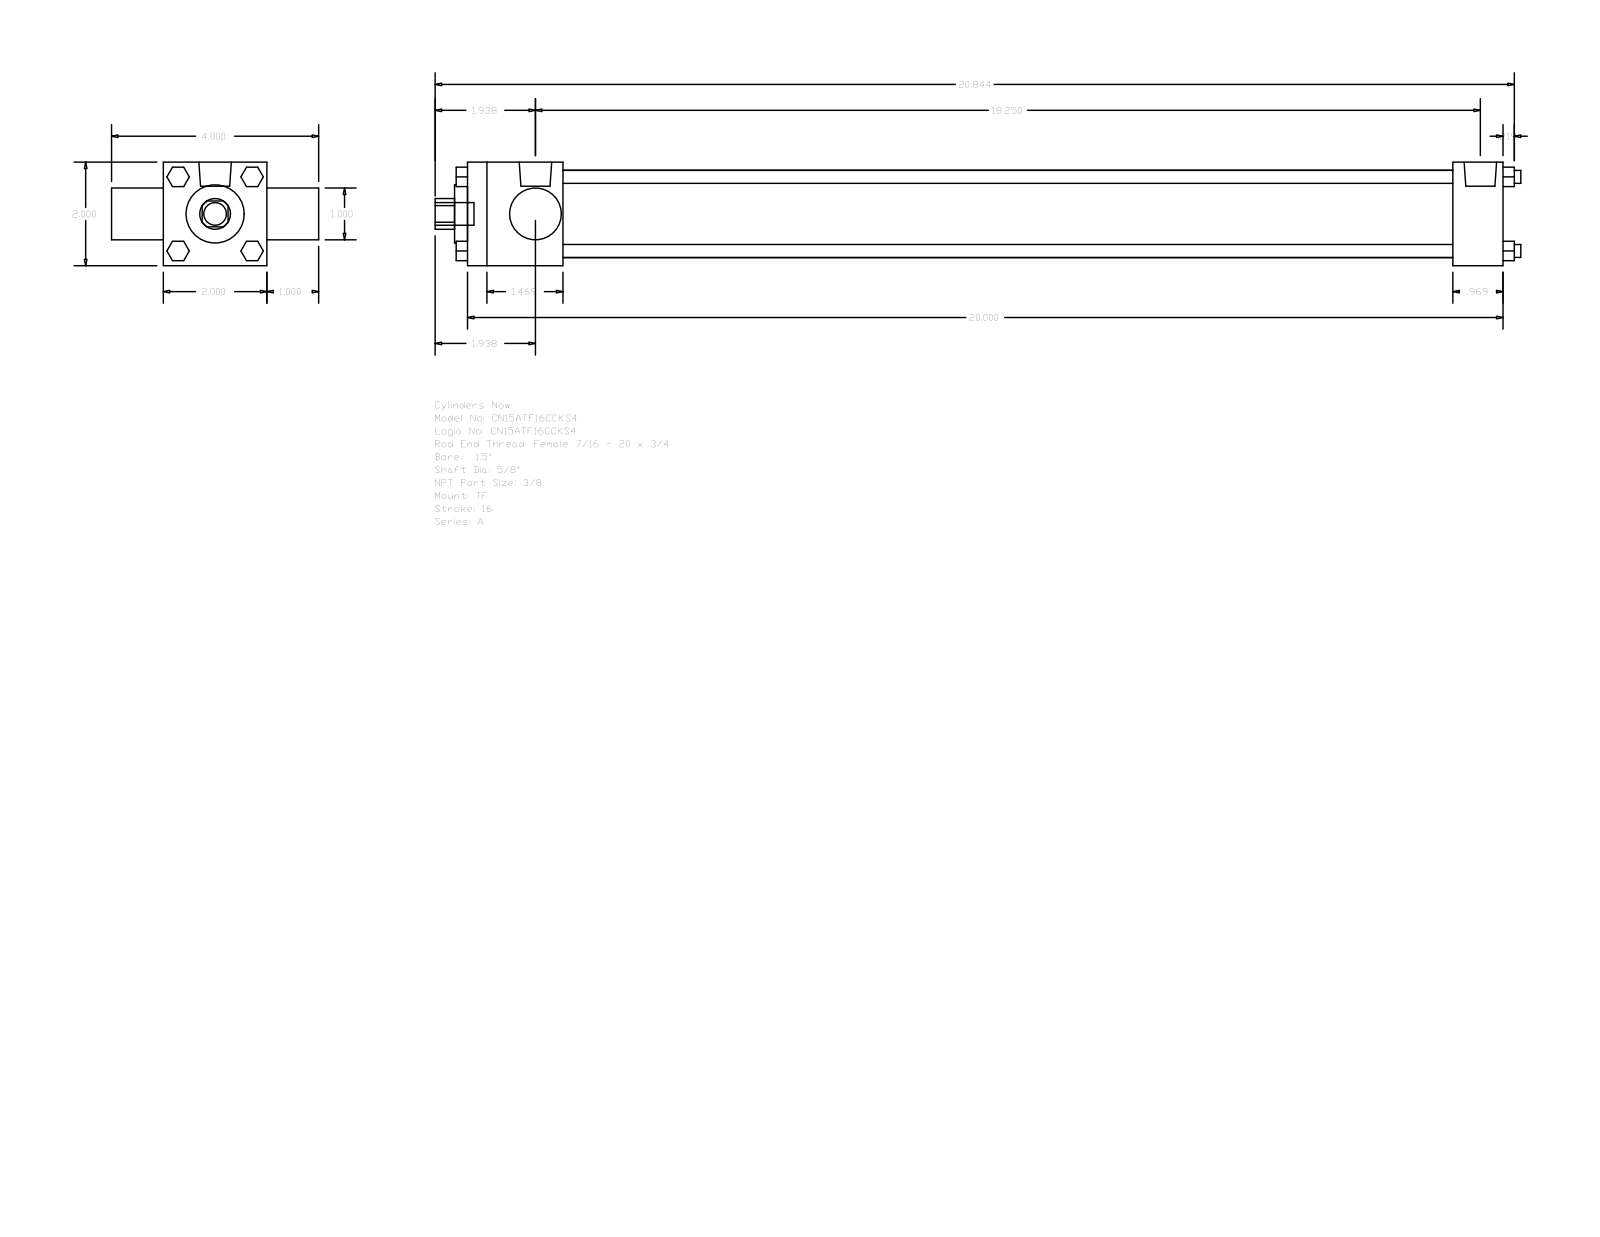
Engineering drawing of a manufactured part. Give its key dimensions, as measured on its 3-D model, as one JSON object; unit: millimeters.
{"part_name": "A_TF__0150_0.625", "step_written_by": "GSSL Pune (CONFIG_CONTROL_DESIGN)", "units": "millimeters", "bodies": {"solids": 0, "faces": 120, "planar": 92, "cylindrical": 28, "other": 0}, "overall_size": [532.61, 101.6, 50.8], "round_holes": [[15.88, 1], [25.4, 1], [28.57, 1], [42.93, 1]], "round_bosses_or_shafts": [[6.35, 4], [5.56, 3], [15.93, 2], [11.11, 1]], "partial_cylinders_radius": [[7.54, 1]], "face_to_face_distances": [50.8, 508, 25.4, 76.2, 46.83, 483.39, 436.56, 461.17, 24.61, 9.52]}
